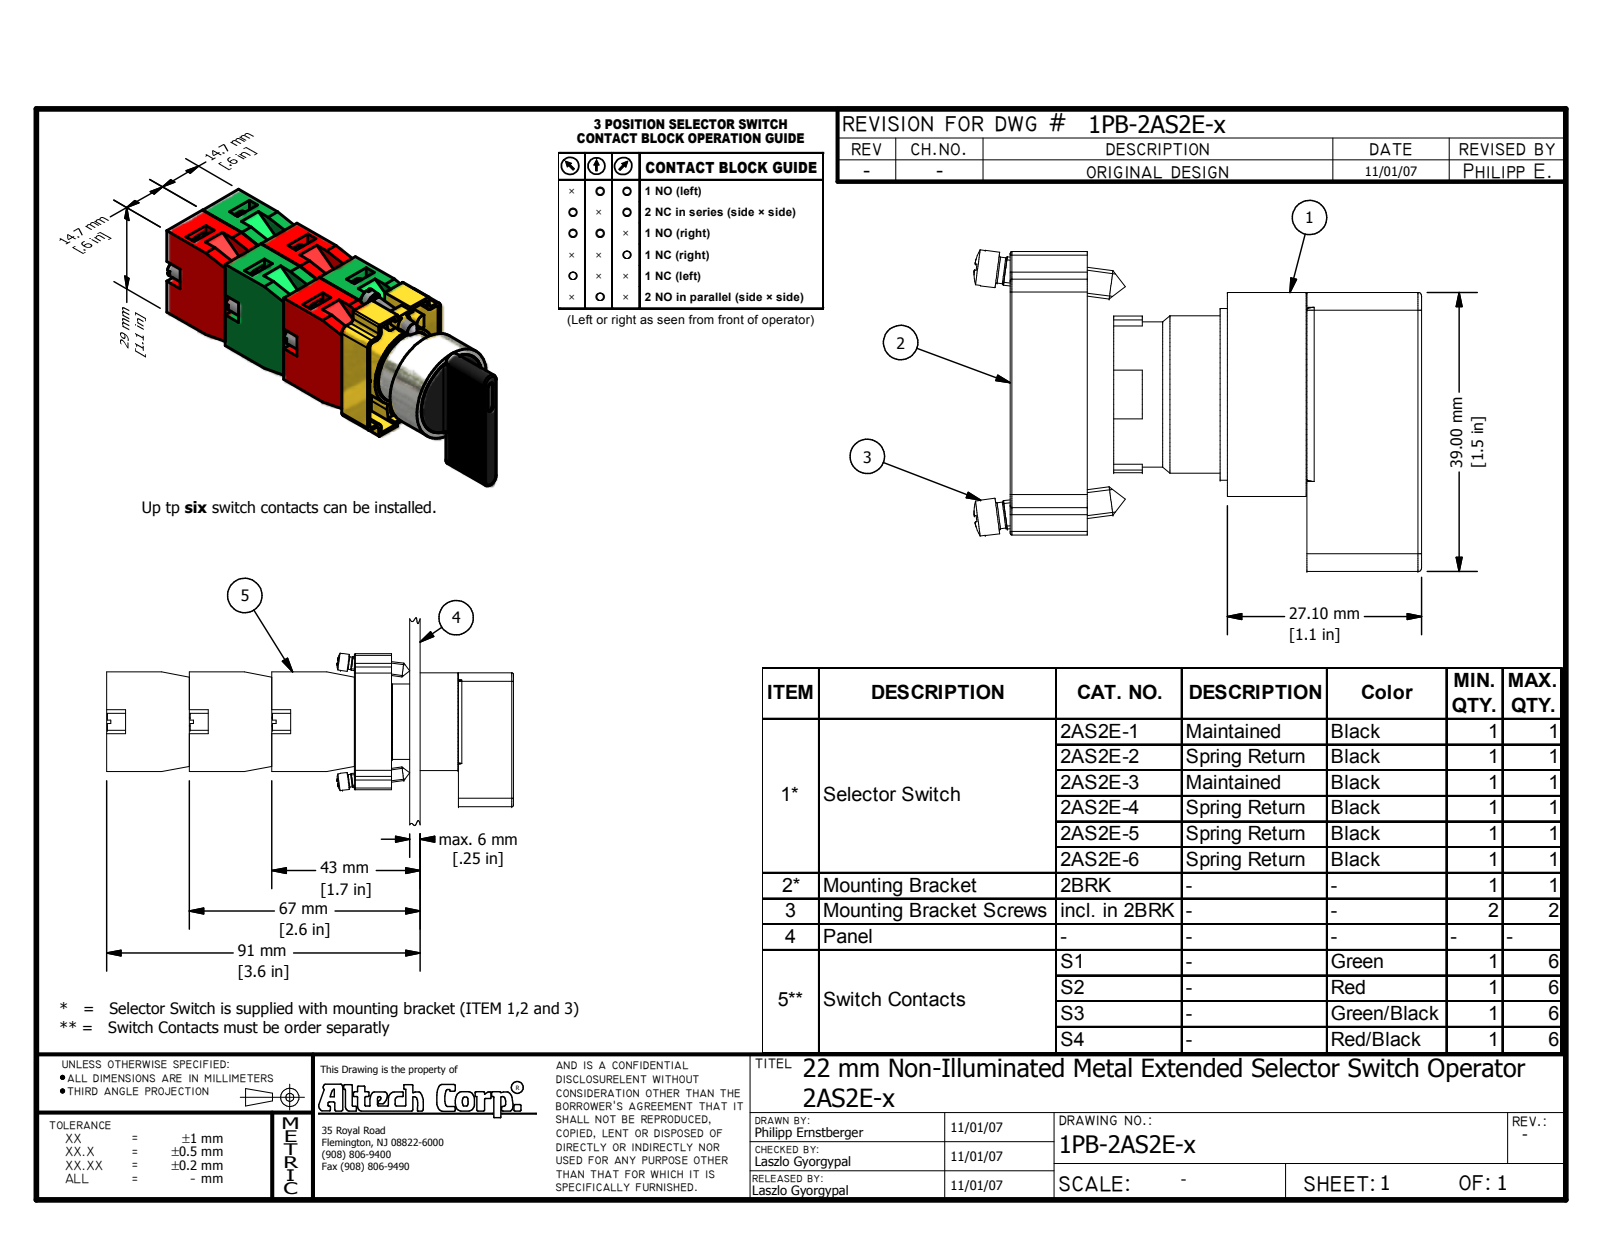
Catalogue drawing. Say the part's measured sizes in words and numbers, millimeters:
The part is named "2AS2E-x_assembly; 2AS2E-x_operator; 2AS2E-x; rubber_gasket (+7 more)". Its 3-D file was written by "Autodesk Inventor 2008 (AUTOMOTIVE_DESIGN)". It is 30 solids with 1230 faces: 674 planar, 199 cylindrical and 357 other. Overall it measures 118.2 by 60.45 by 45 millimeters. Its volume is 75 819 cubic millimeters and its surface area 47 126 square millimeters. Round holes: 5 of diameter 2.5, 2 of diameter 2.6, 1 of diameter 13.5, 1 of diameter 17.75, 1 of diameter 22, 1 of diameter 22.25, 1 of diameter 22.5, 1 of diameter 25, 1 of diameter 26.5. Round bosses or shafts: 6 of diameter 3, 4 of diameter 5, 4 of diameter 2.75, 4 of diameter 1.5, 2 of diameter 4, 2 of diameter 3.65, 1 of diameter 28.5, 1 of diameter 24.8. Partial cylindrical surfaces (rounded edges, fillets, slot ends): 17 of radius 1, 13 of radius 0.25, 8 of radius 0.72, 6 of radius 0.5, 5 of radius 2.25, 4 of radius 0.8, 4 of radius 1.8, 4 of radius 2. The main face-to-face distances are 14.8, 14.7, 24, 3, 48, 29.5, 29, 1, 19.1, 16.1. The hole center spacings are 14.53, 6.52, 6.57, 13, 25.88, 26, 26.27, 29.07.
